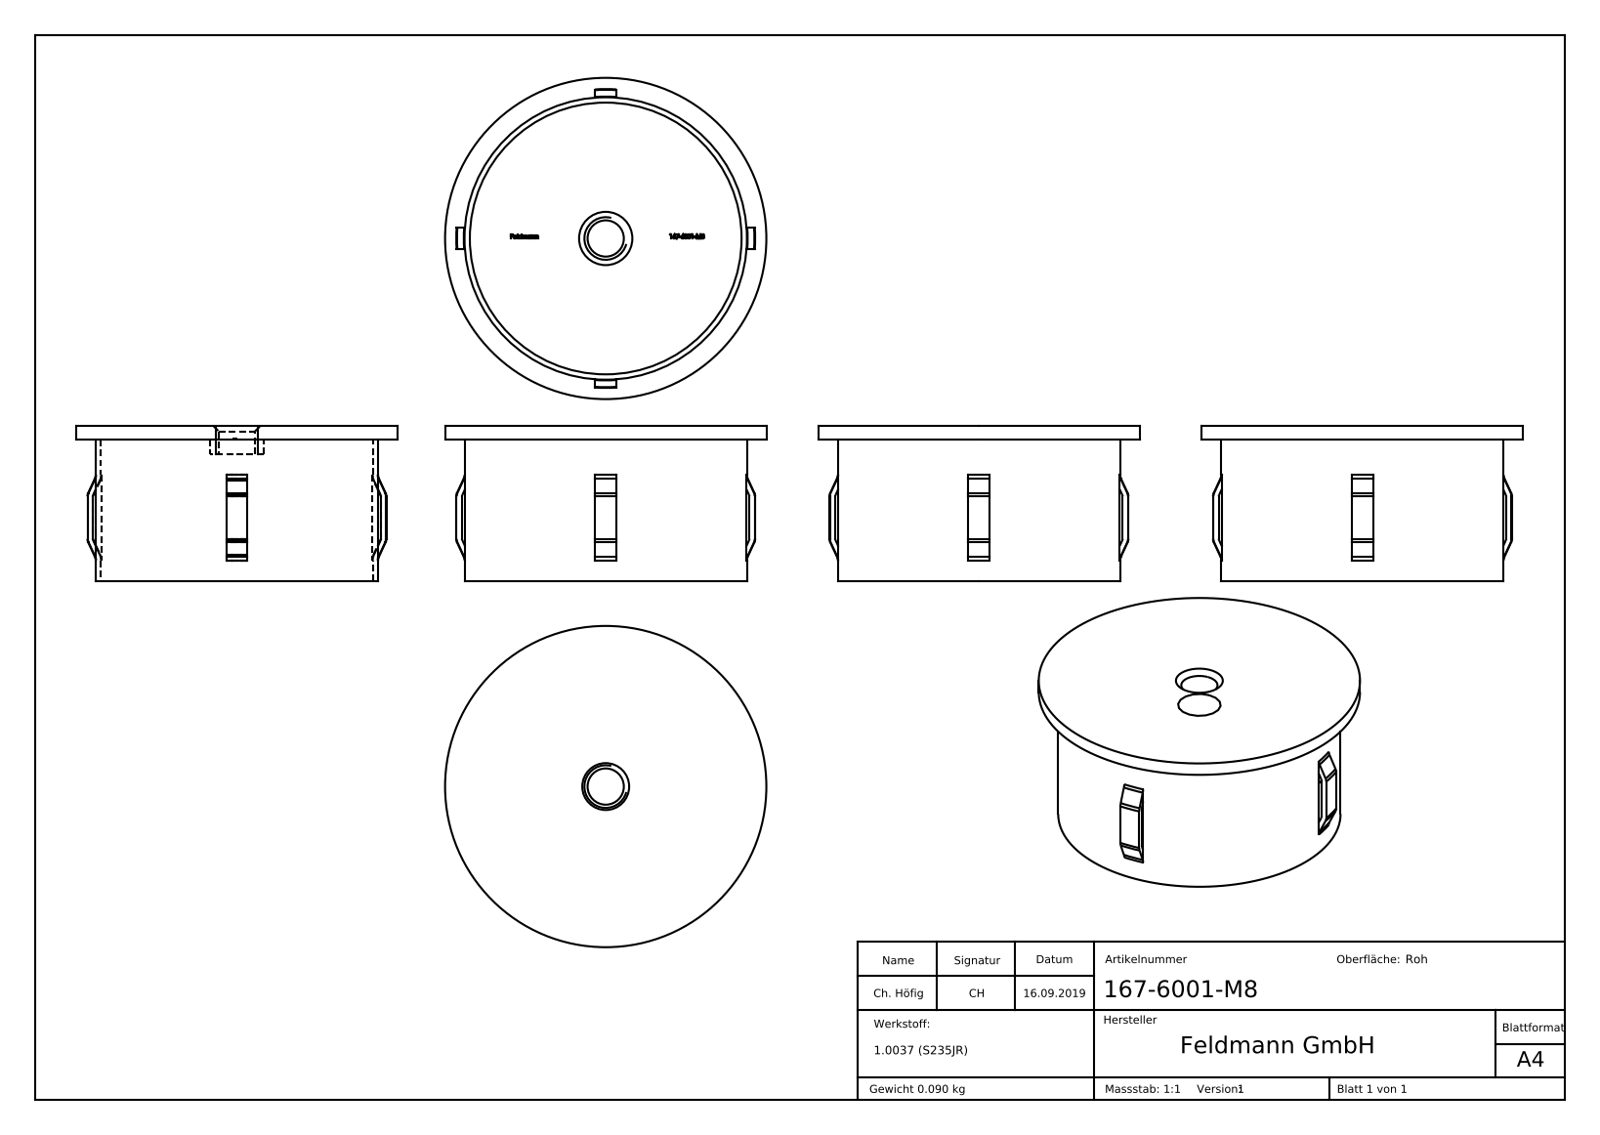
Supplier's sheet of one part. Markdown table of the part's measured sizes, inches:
| quantity | value |
| --- | --- |
| part name | 167-6001-M8 |
| STEP written by | SolidWorks 2015 (CONFIG_CONTROL_DESIGN) |
| units | inches |
| bodies | 1 solid, 331 faces (148 planar, 20 cylindrical, 163 other) |
| overall size | 2.374 × 2.374 × 1.15 |
| volume | 0.703 in³ |
| surface area | 23.66 in² |
| round holes (diameter × count) | 0.268 × 1, 2.008 × 1 |
| round bosses / shafts (diameter × count) | 2.374 × 1, 2.087 × 1, 0.394 × 1 |
| partial cylindrical surfaces (radius × count) | 1.065 × 1, 1.104 × 1 |
| main face-to-face distances | 0.098, 1.051, 1.15, 0.157, 0.941, 0.11, 0.209, 1.055, 0.114, 0.094 |
